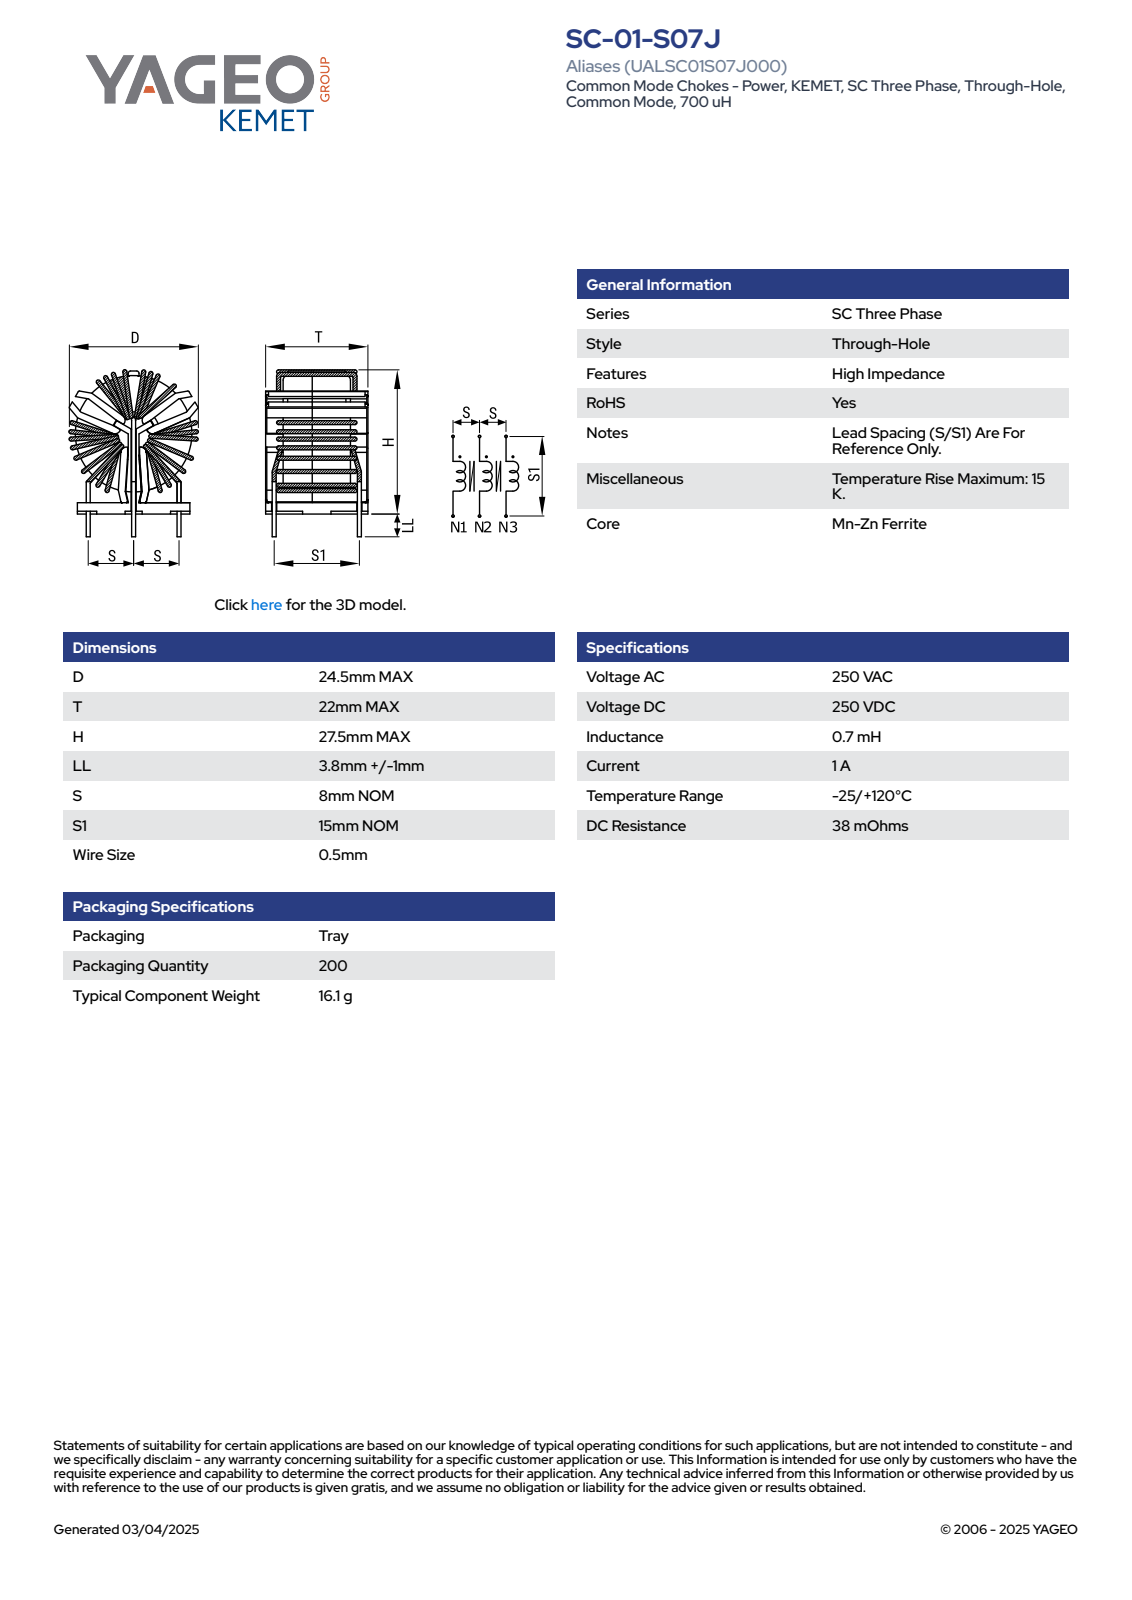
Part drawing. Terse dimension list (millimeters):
name: SC-01-S07J
written by: SolidWorks 2018 (AUTOMOTIVE_DESIGN)
unit: mm
bodies: 1 solid, 636 faces (280 planar, 208 cylindrical, 148 other)
size: 31.3 × 24.5 × 22
volume: 7 876 mm³; area: 6 678 mm²
bosses: 10× ⌀0.5
rounds: 92× R0.2, 25× R0.25, 6× R0.45, 6× R1, 1× R2.85, 1× R3.85, 1× R4.65, 1× R4.9
face distances: 2.65, 4, 18, 1.08, 14, 1.4, 0.5, 1.05, 1.25, 1
